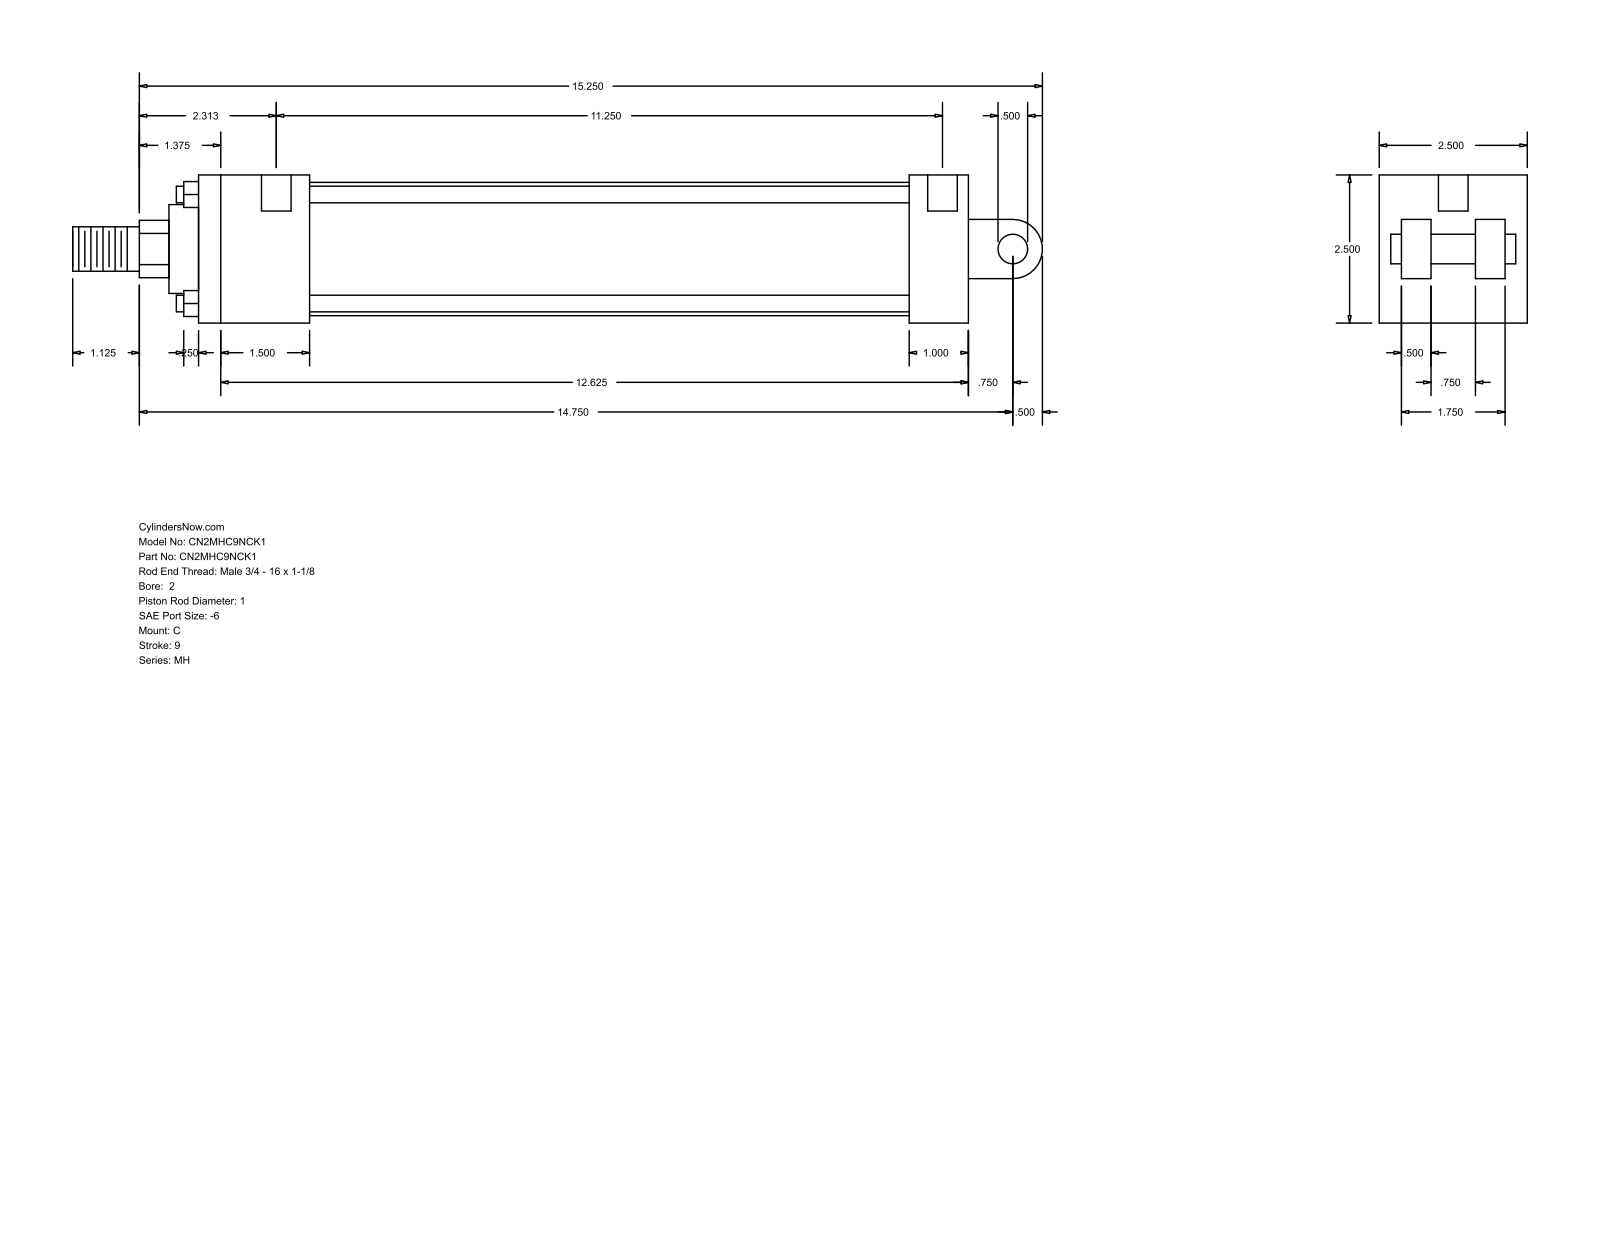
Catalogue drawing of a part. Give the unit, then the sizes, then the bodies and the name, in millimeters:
Units: millimetres
Overall size (bounding box): 415.93 × 63.5 × 63.5
Round holes (diameter × count): ⌀5.56 ×4, ⌀12.7 ×2
Round bosses / shafts (diameter × count): ⌀7.14 ×4, ⌀57.15 ×1, ⌀38.1 ×1, ⌀25.4 ×1, ⌀19.05 ×1, ⌀12.7 ×1
Partial cylindrical surfaces — rounded edges, fillets, slot ends (radius × count): R12.29 ×1, R12.7 ×1
Main face-to-face distances: 63.5, 330.2, 12.7, 25.4, 47.63, 53.98, 9.52, 304.8, 257.17, 282.57
Hole centre spacings: 293.68, 3.17, 4.76, 285.75, 288.92, 290.51
Bodies: 0 solids, 99 faces (70 planar, 29 cylindrical, 0 other)
Part name (STEP PRODUCT): MH_C__0200_1
STEP written by: GSSL Pune (CONFIG_CONTROL_DESIGN)
